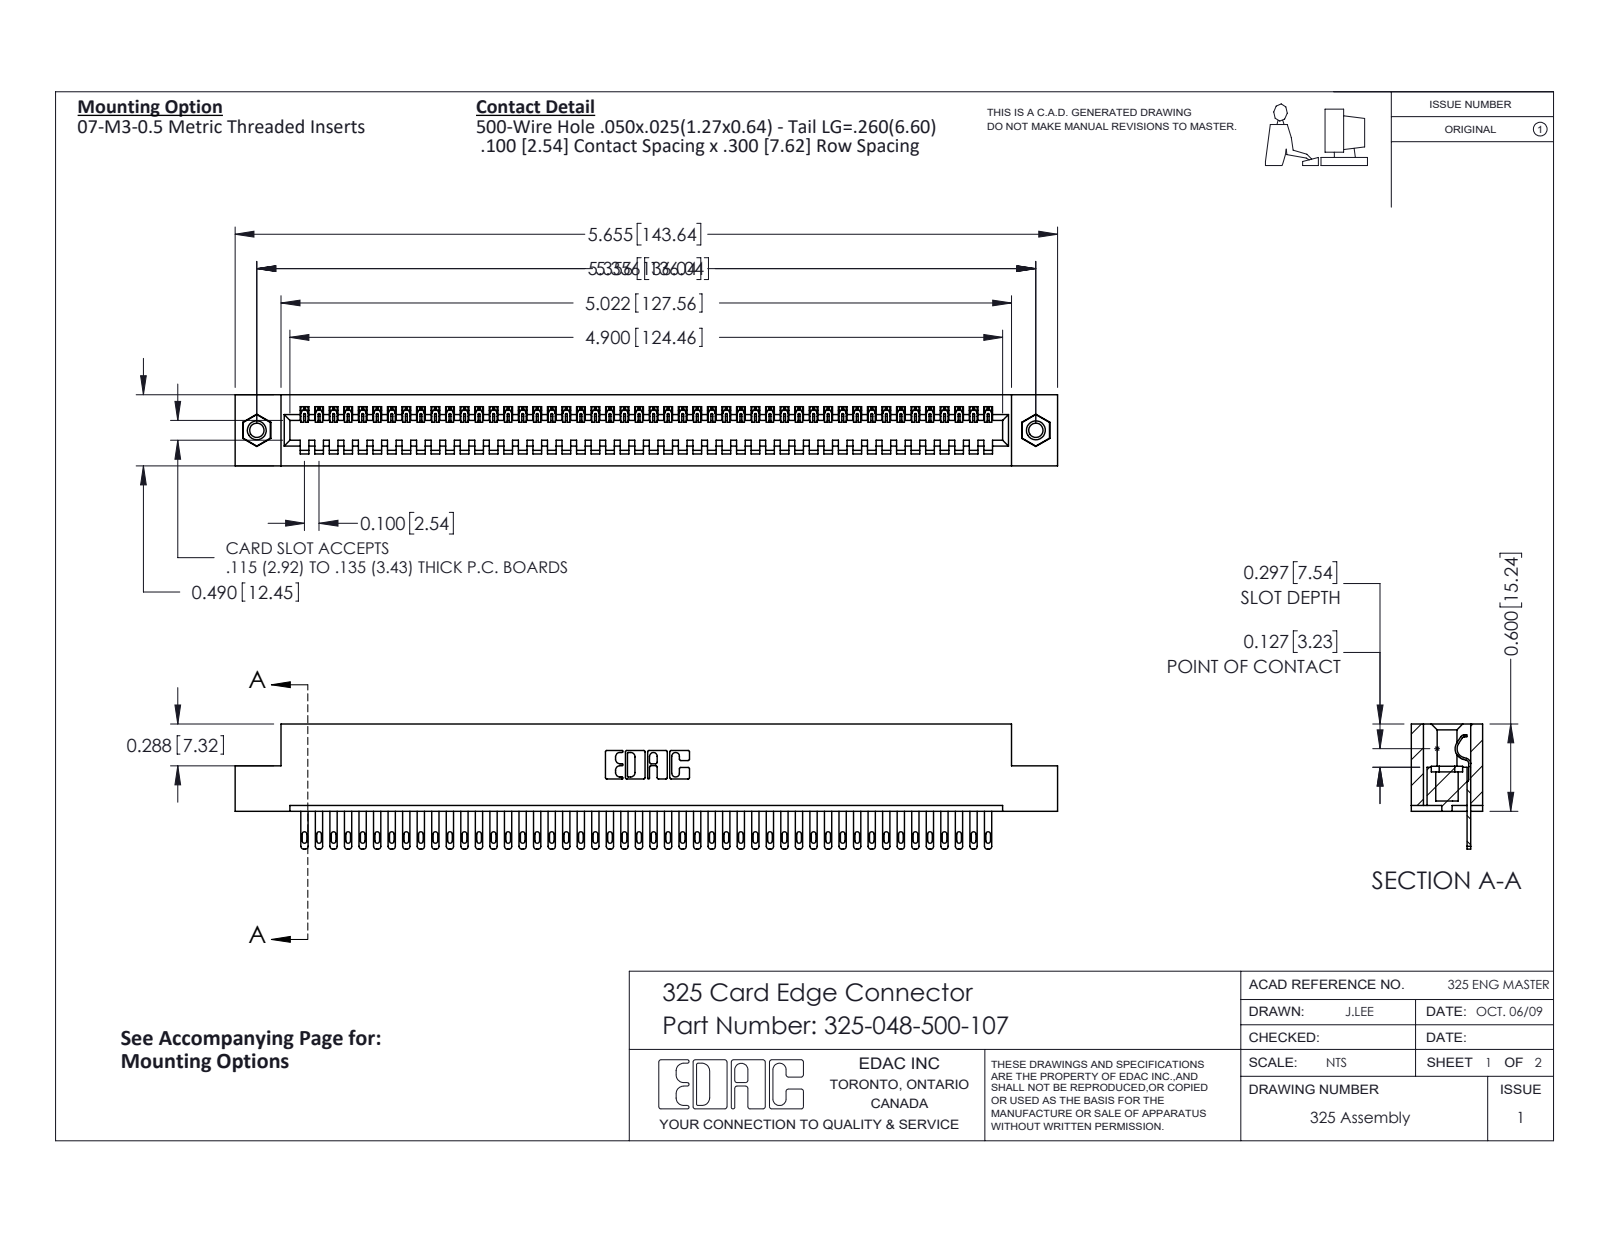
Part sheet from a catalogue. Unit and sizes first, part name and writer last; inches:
Units: inches
Overall size (bounding box): 5.655 × 0.86 × 0.49
Round holes (diameter × count): ⌀0.098 ×2, ⌀0.125 ×2, ⌀0.16 ×2
Round bosses / shafts (diameter × count): ⌀0.155 ×2
Partial cylindrical surfaces — rounded edges, fillets, slot ends (radius × count): R0.006 ×96, R0.016 ×96, R0.02 ×96, R0.01 ×22, R0.007 ×6, R0.031 ×6, R0.026 ×3, R0.014 ×1
Main face-to-face distances: 0.083, 0.407, 0.49, 0.3, 0.107, 0.383, 0.025, 0.325, 0.56, 0.263
Hole centre spacings: 5.356
Volume: 1.117 in³ · Surface area: 31.36 in²
Bodies: 51 solids, 2766 faces (1830 planar, 920 cylindrical, 16 other)
Part name (STEP PRODUCT): 325-292-001_325-293-100; 325-048-500-107; 345-250-001_345-250-005-103; 325 Part_TI
STEP written by: SolidWorks 2016 (CONFIG_CONTROL_DESIGN)
